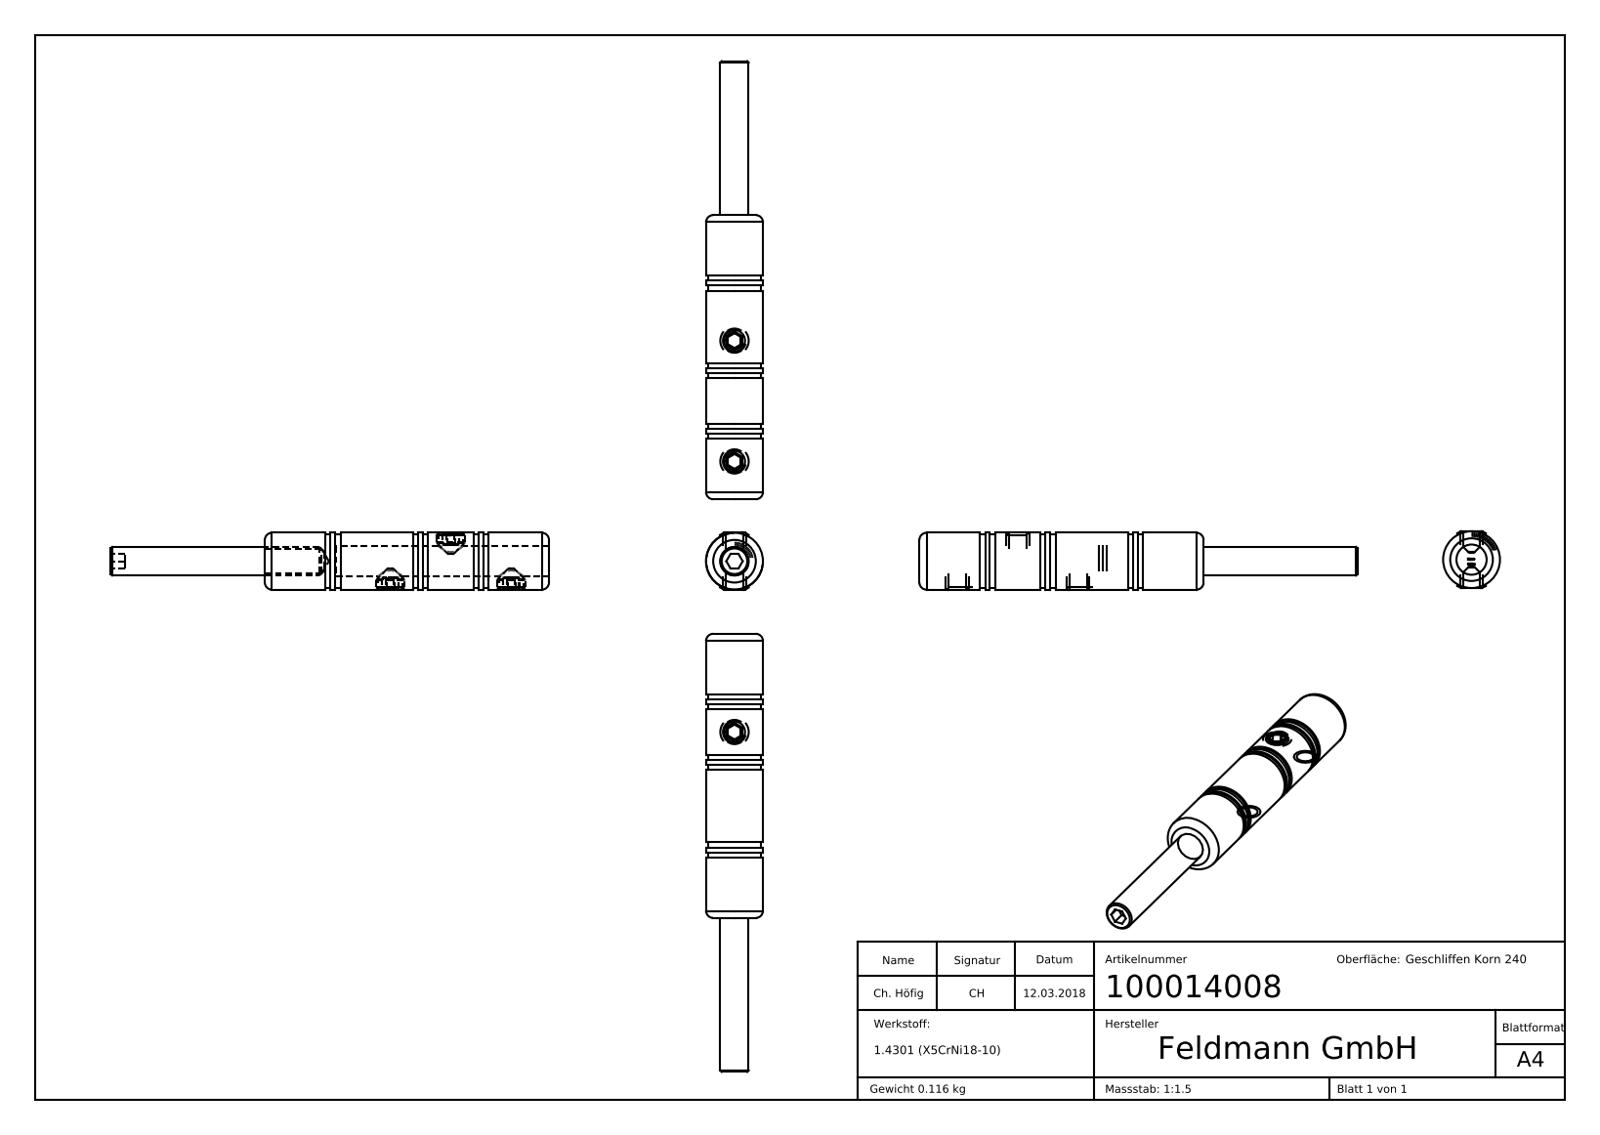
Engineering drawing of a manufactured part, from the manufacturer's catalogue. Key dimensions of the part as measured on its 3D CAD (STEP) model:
Part name (STEP PRODUCT): DIN914_DIN 914 M8x6; 10001X00X Teil 1_100014008 Teil1; 100014008; DIN913_DIN913 M8x60
STEP written by: SolidWorks 2015 (CONFIG_CONTROL_DESIGN)
Units: millimetres
Bodies: 5 solids, 436 faces (158 planar, 98 cylindrical, 180 other)
Overall size (bounding box): 123.35 × 16 × 16
Volume: 14 733 mm³ · Surface area: 8 891 mm²
Round holes (diameter × count): ⌀6.8 ×4, ⌀8.5 ×1
Round bosses / shafts (diameter × count): ⌀8 ×4, ⌀16 ×1, ⌀15 ×1
Partial cylindrical surfaces — rounded edges, fillets, slot ends (radius × count): R0.2 ×50
Main face-to-face distances: 1.5, 2.8, 17, 41.7, 4, 1.3, 18.5, 19.8, 24.7, 60
Hole centre spacings: 17, 34
